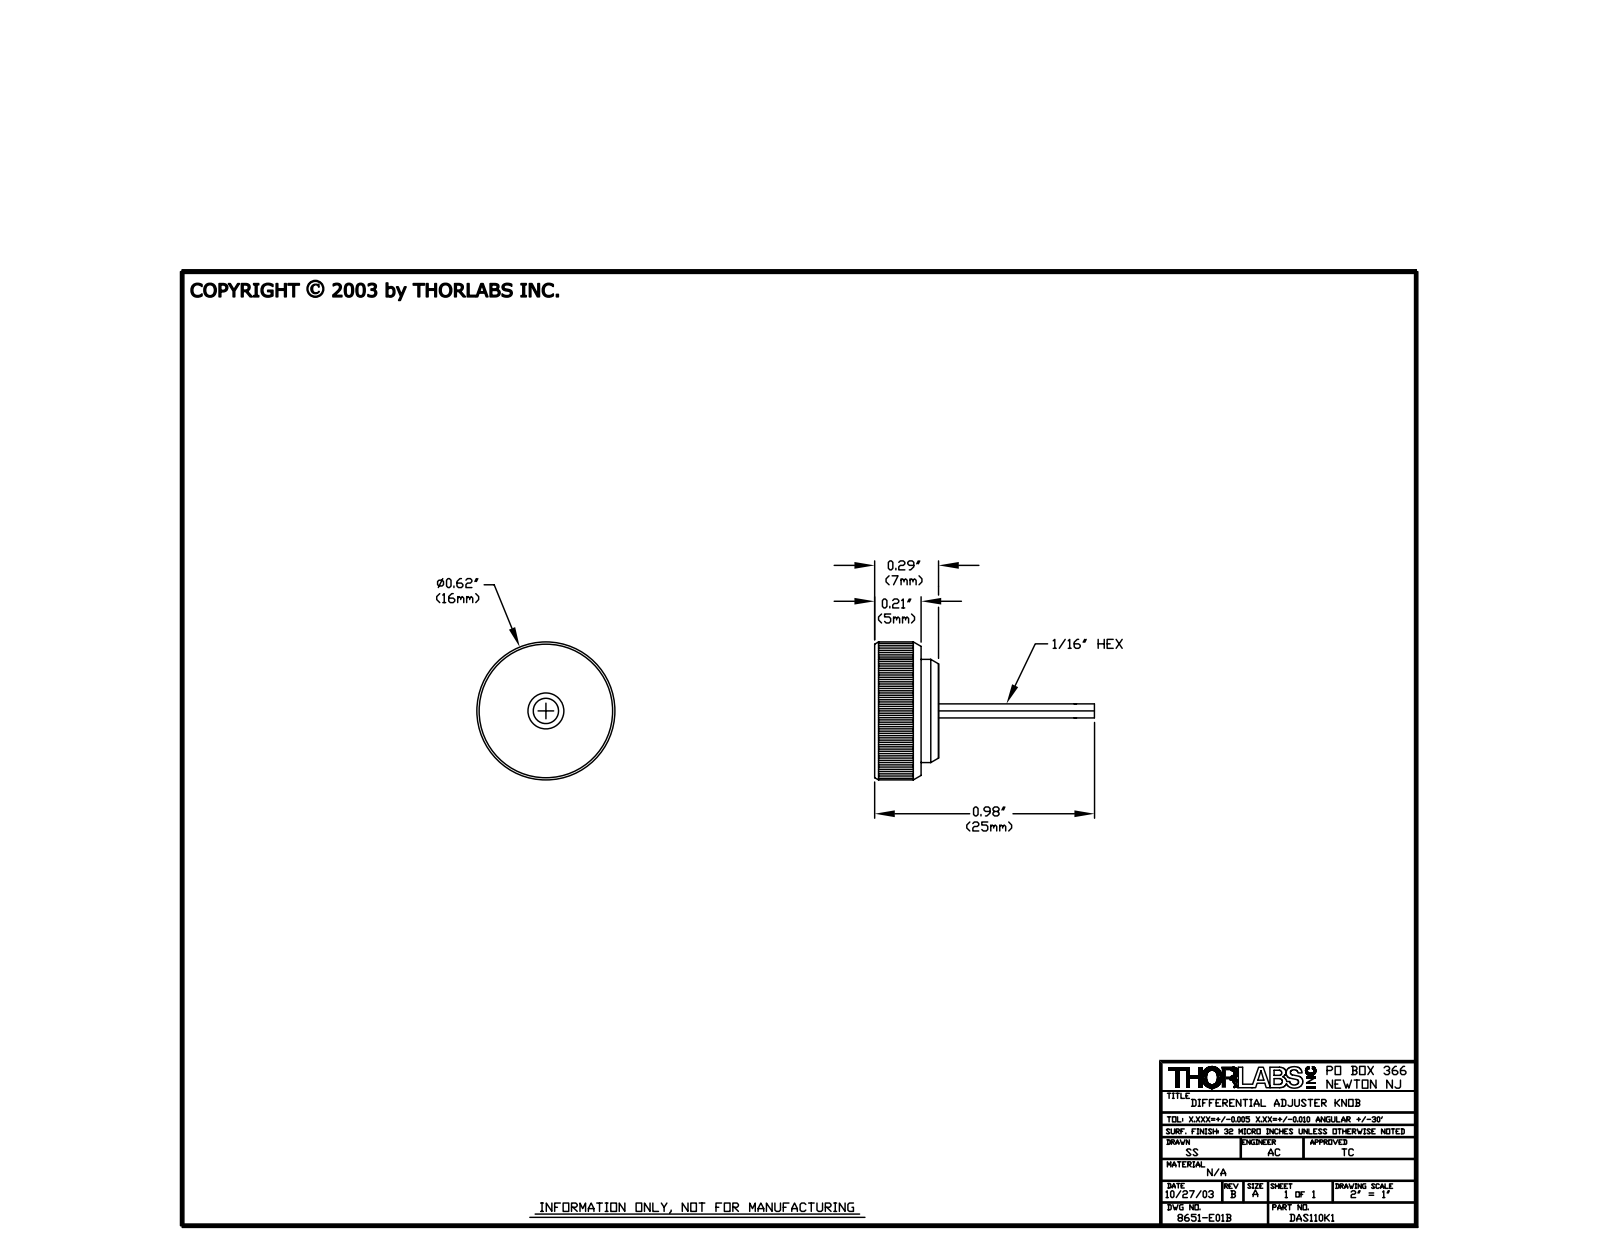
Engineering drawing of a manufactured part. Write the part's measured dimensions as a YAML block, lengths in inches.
part_name: "8651-E0W"
step_written_by: "SolidWorks 2007 (AUTOMOTIVE_DESIGN)"
units: inches
bodies: {solids: 0, faces: 25, planar: 11, cylindrical: 8, other: 6}
overall_size: [0.975, 0.615, 0.615]
round_holes:
  - {diameter: 0.069, count: 1}
  - {diameter: 0.113, count: 1}
round_bosses_or_shafts:
  - {diameter: 0.615, count: 1}
  - {diameter: 0.458, count: 1}
face_to_face_distances: [0.285, 0.078, 0.207, 0.055, 0.054, 0.245, 0.167, 0.04, 0.69, 0.768]
